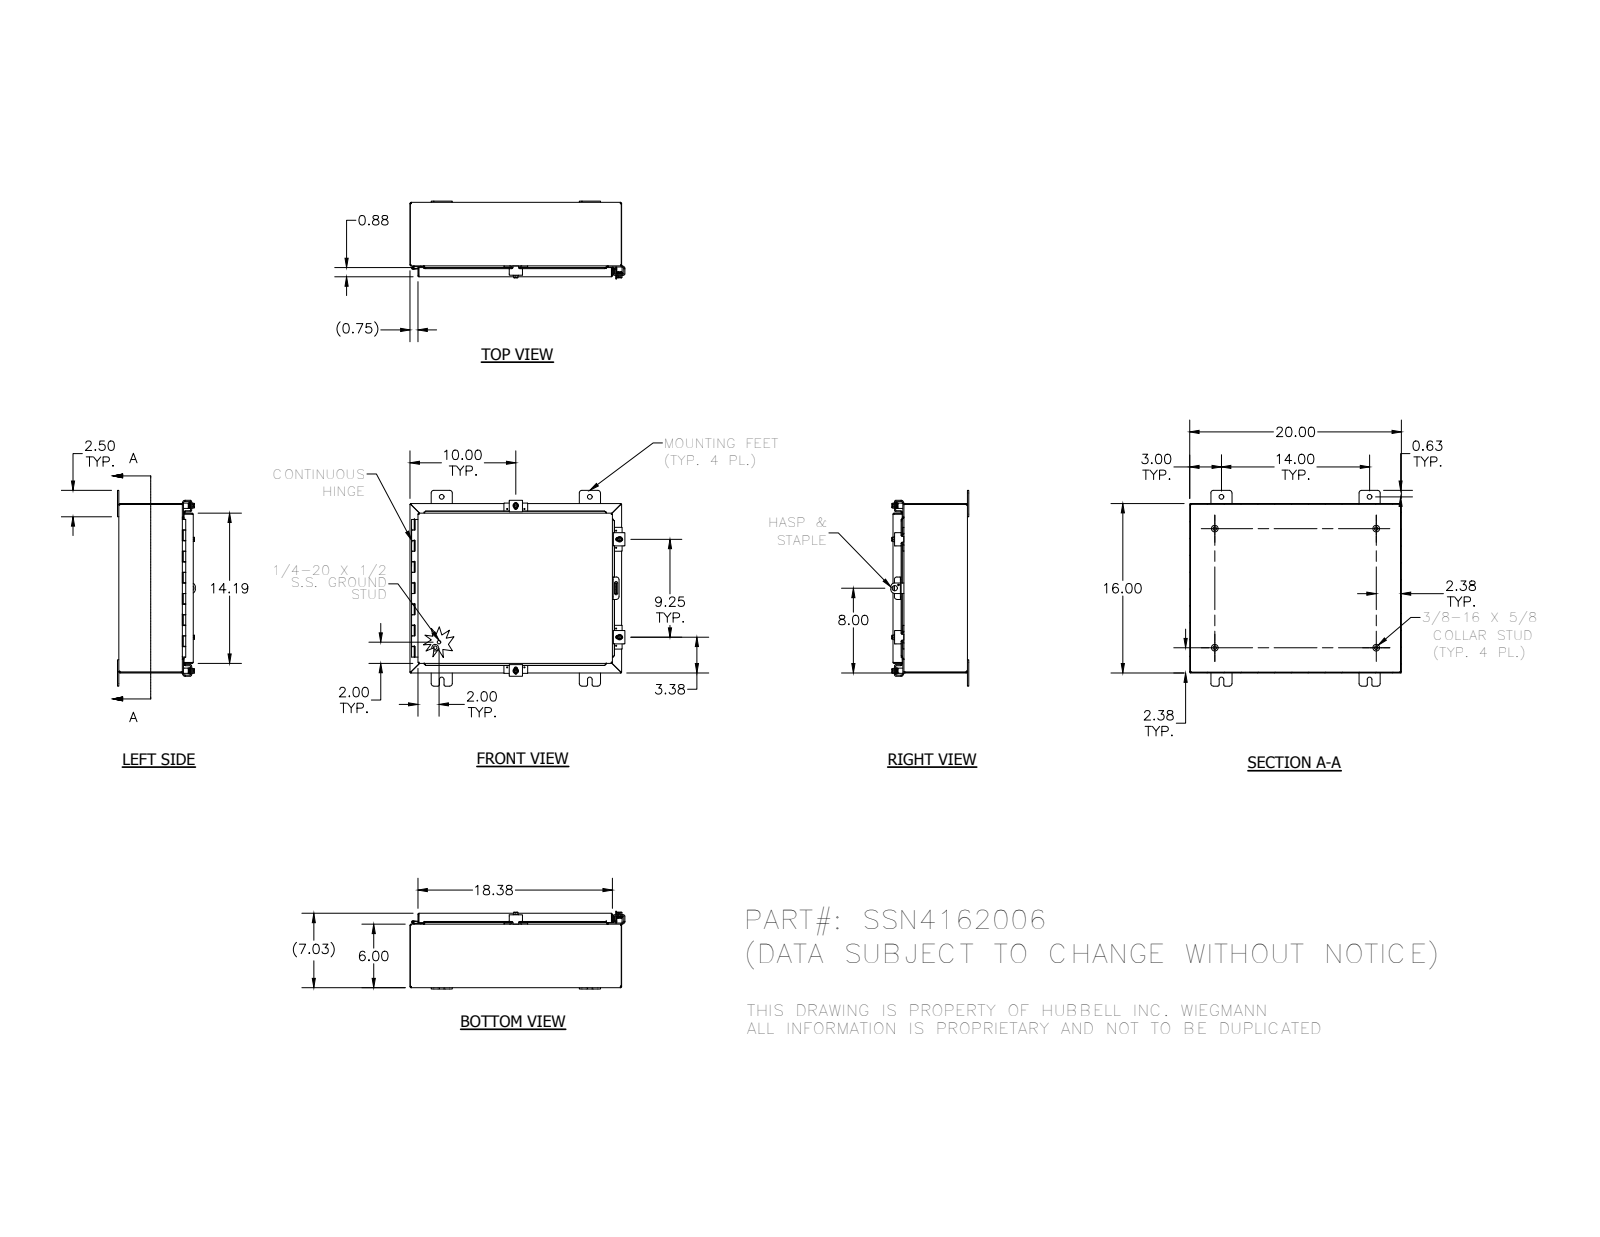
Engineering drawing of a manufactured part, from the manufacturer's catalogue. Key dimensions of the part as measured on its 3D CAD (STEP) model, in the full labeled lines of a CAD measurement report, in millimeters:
Part name (STEP PRODUCT): 38859_1; 34871_1; 14x18_1; 38846_1 (+8 more)
STEP written by: SolidWorks 2014 (AUTOMOTIVE_DESIGN)
Units: millimetres
Bodies: 37 solids, 1390 faces (545 planar, 604 cylindrical, 241 other)
Overall size (bounding box): 515.9 × 469.9 × 186.8
Volume: 1 693 000 mm³ · Surface area: 1 732 000 mm²
Round holes (diameter × count): ⌀2.8 ×8, ⌀5.4 ×4, ⌀7.1 ×4, ⌀7.6 ×4, ⌀11.1 ×4, ⌀3.2 ×1, ⌀4 ×1, ⌀12.7 ×1
Round bosses / shafts (diameter × count): ⌀6.4 ×6, ⌀15.9 ×4, ⌀13.2 ×4, ⌀12.7 ×4, ⌀8.9 ×4, ⌀8.4 ×4, ⌀8.6 ×1, ⌀3 ×1
Partial cylindrical surfaces — rounded edges, fillets, slot ends (radius × count): R0.8 ×49, R3.2 ×33, R6.4 ×29, R0.8 ×23, R2.7 ×23, R1.6 ×11, R1.8 ×8, R3.6 ×8
Main face-to-face distances: 1.9, 176.8, 174.9, 178.6, 404.5, 506.1, 150.5, 26.2, 402.6, 406.4
Hole centre spacings: 22.3, 388.9, 235, 22.3, 41.3, 41.3, 157.2, 159.8
